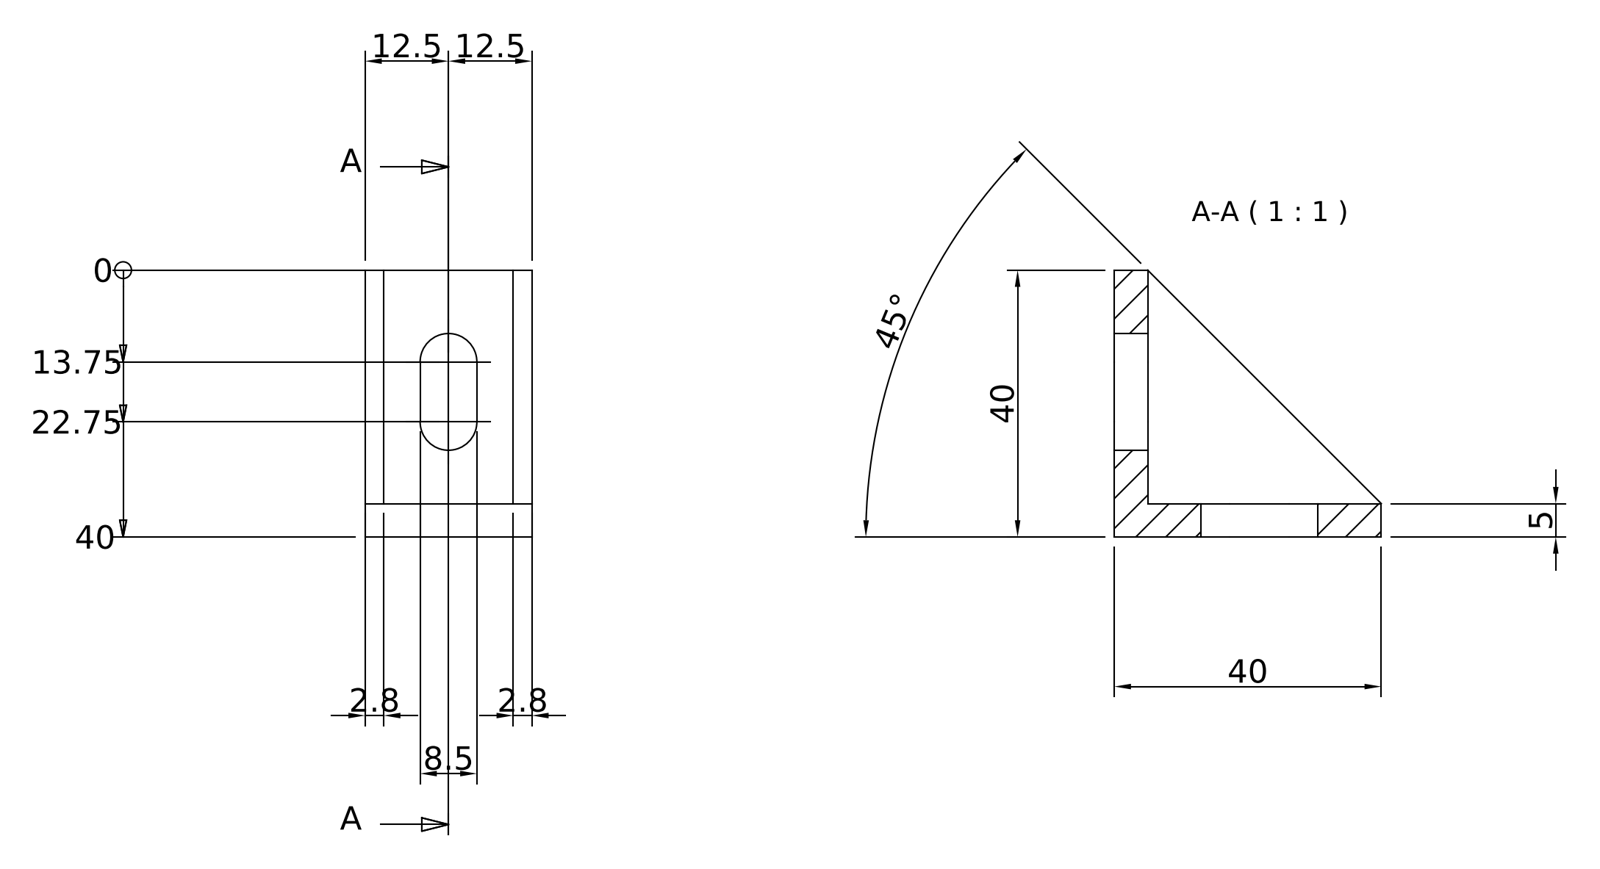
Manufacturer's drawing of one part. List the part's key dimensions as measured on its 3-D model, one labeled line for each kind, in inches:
Part name (STEP PRODUCT): DSQAL0000005
STEP written by: Autodesk Inventor 2022 (AUTOMOTIVE_DESIGN)
Units: inches
Bodies: 1 solid, 20 faces (16 planar, 4 cylindrical, 0 other)
Overall size (bounding box): 1.575 × 1.575 × 0.984
Volume: 0.7 in³ · Surface area: 10.85 in²
Partial cylindrical surfaces — rounded edges, fillets, slot ends (radius × count): R0.167 ×4
Main face-to-face distances: 0.11, 0.874, 0.197, 0.984, 0.764, 1.378, 1.575, 0.325, 0.659, 0.215
